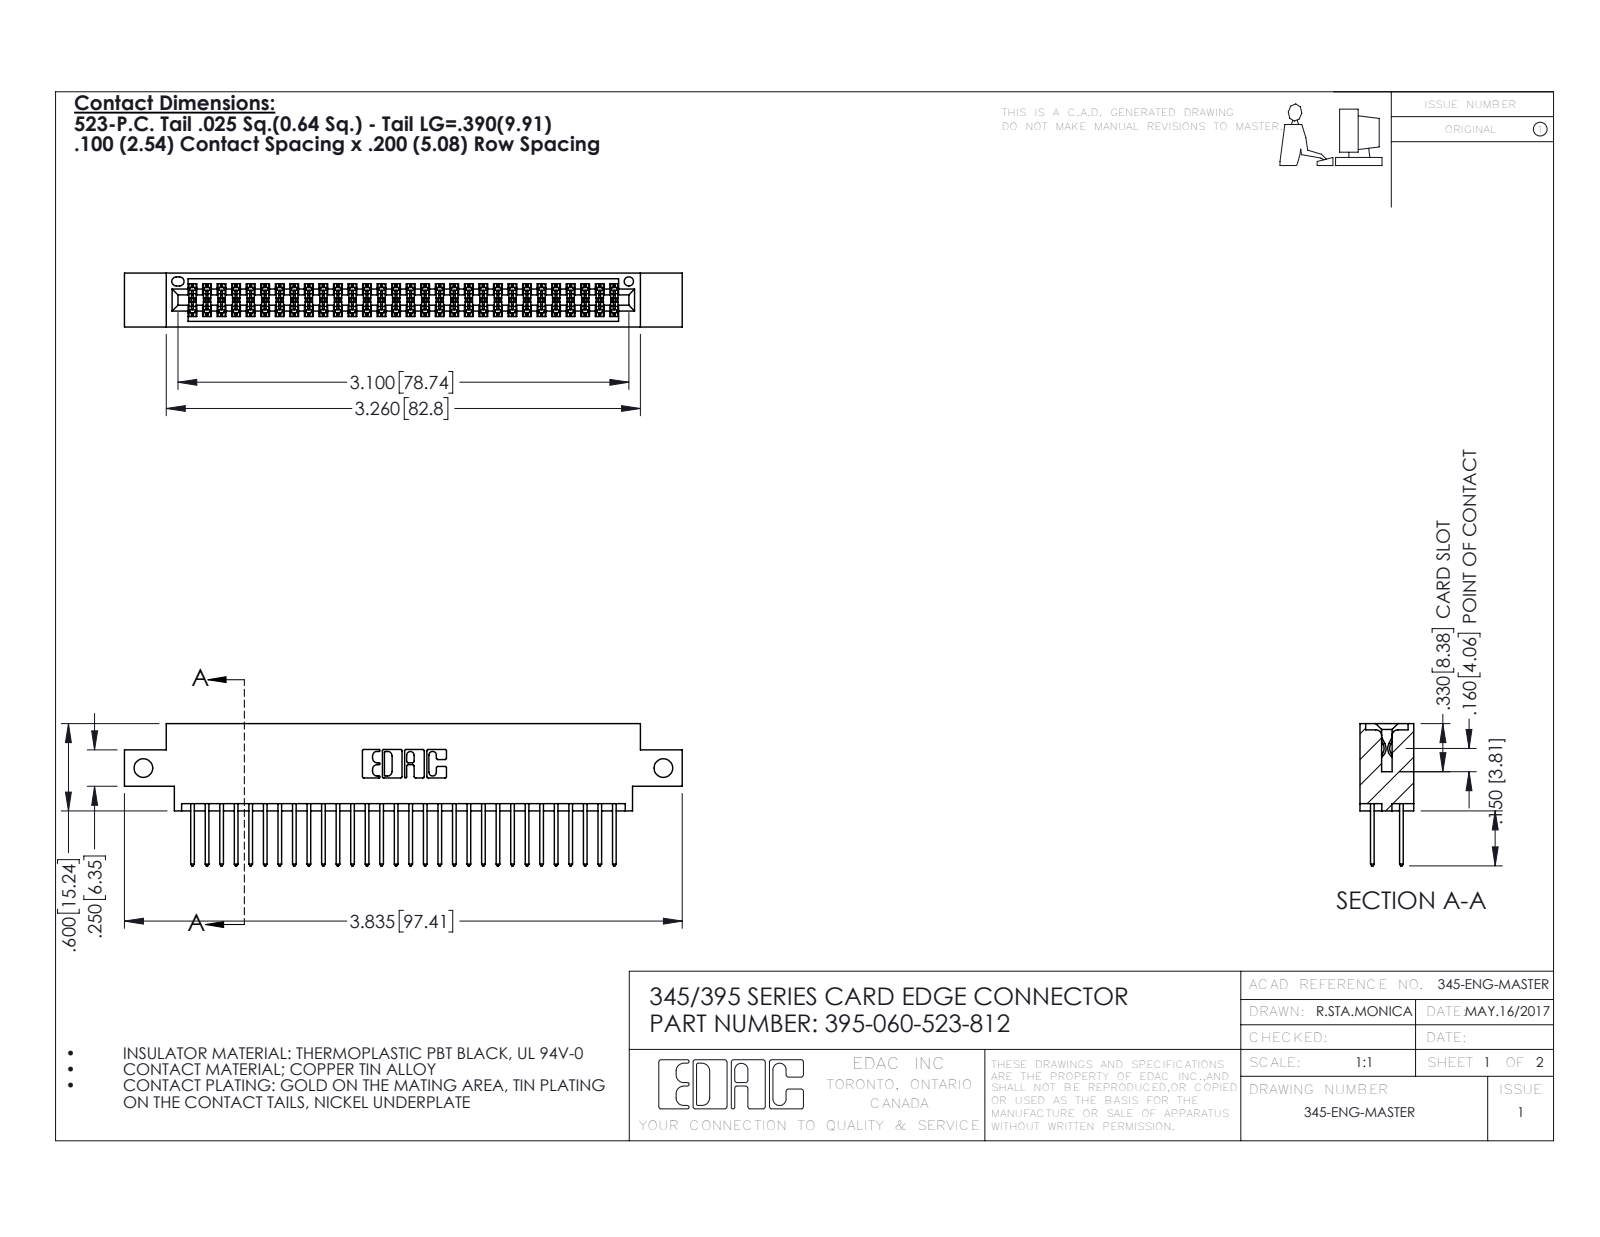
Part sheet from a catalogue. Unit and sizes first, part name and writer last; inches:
Units: inches
Overall size (bounding box): 3.835 × 0.977 × 0.37
Round holes (diameter × count): ⌀0.128 ×2, ⌀0.064 ×1
Partial cylindrical surfaces — rounded edges, fillets, slot ends (radius × count): R0.006 ×90, R0.01 ×60, R0.01 ×22, R0.007 ×6, R0.031 ×6, R0.026 ×3, R0.014 ×2, R0.019 ×2
Main face-to-face distances: 0.298, 0.072, 0.2, 0.098, 0.272, 0.025, 0.37, 0.225, 0.175, 0.149
Hole centre spacings: 3.575
Volume: 0.566 in³ · Surface area: 21.75 in²
Bodies: 61 solids, 3130 faces (2064 planar, 1066 cylindrical, 0 other)
Part name (STEP PRODUCT): 395-060-523-812; 345 Part_0.170 Offset - Side Mount; 345-292-001_345-293-123
STEP written by: SolidWorks 2016 (CONFIG_CONTROL_DESIGN)
